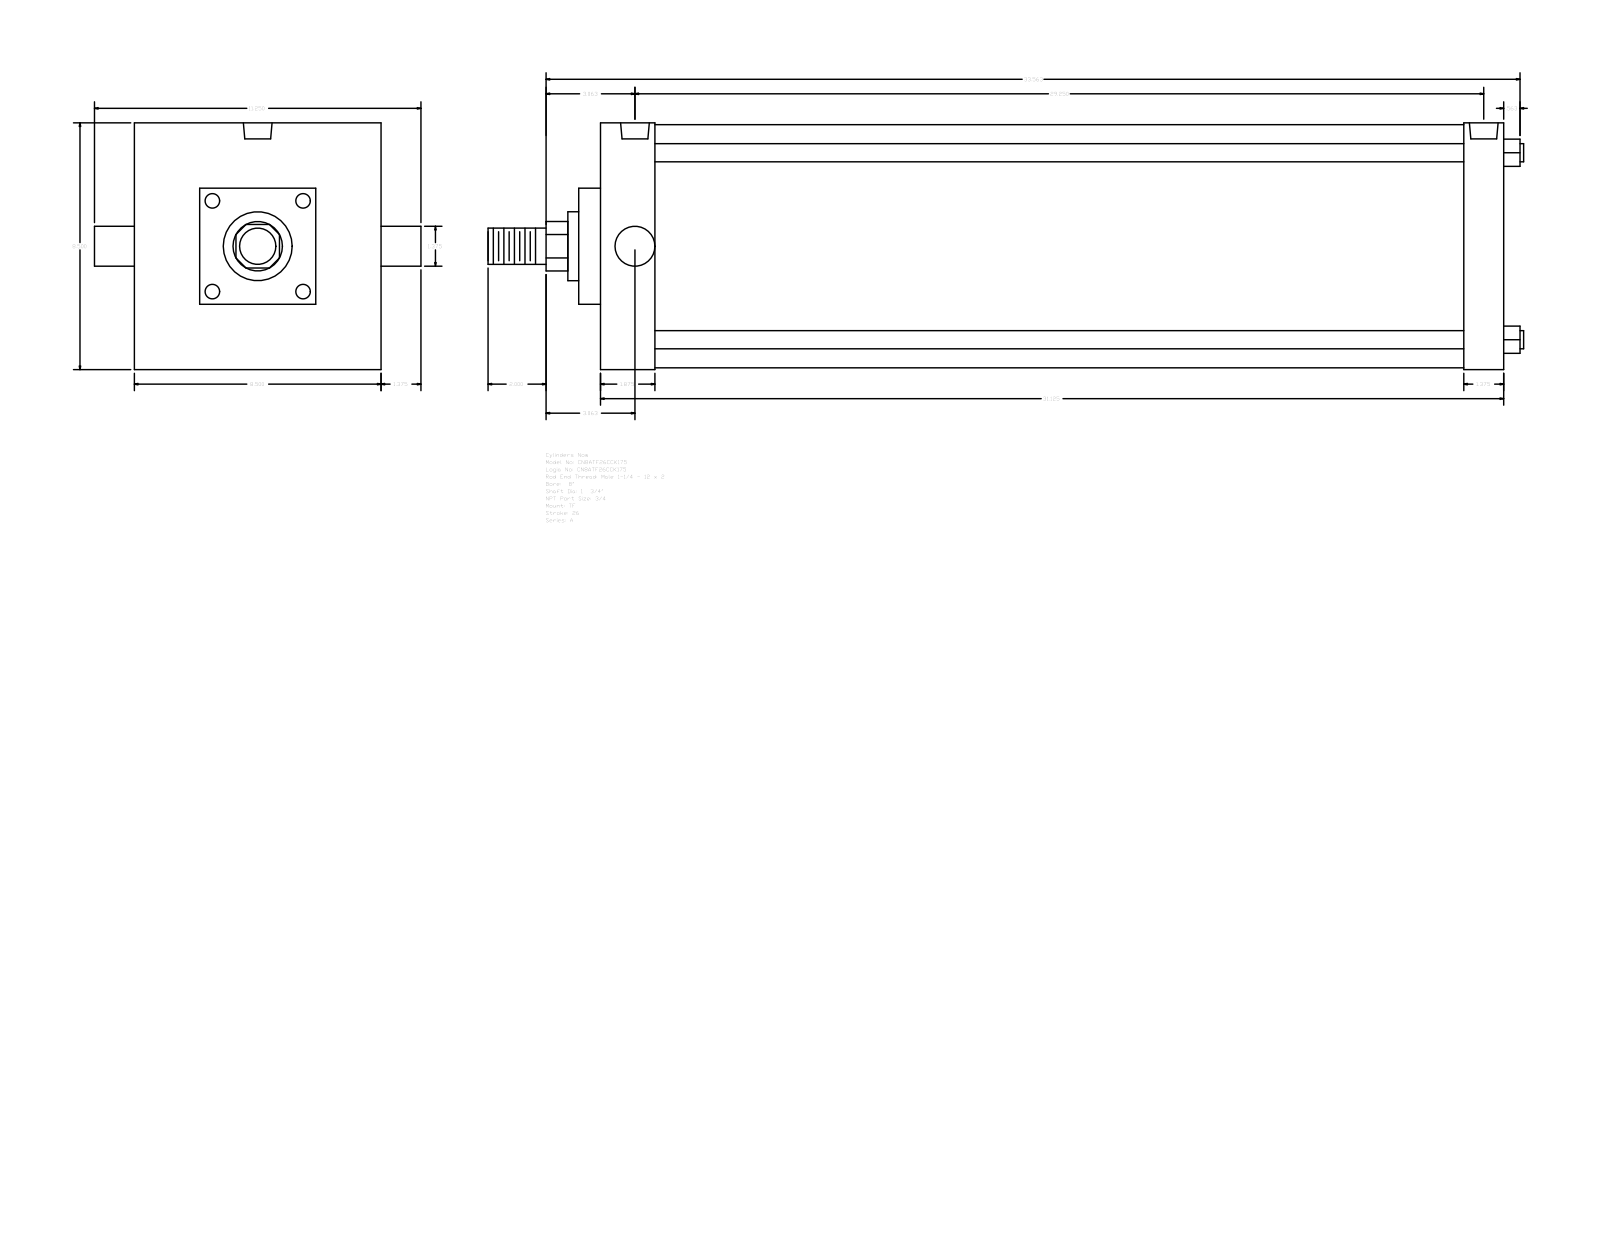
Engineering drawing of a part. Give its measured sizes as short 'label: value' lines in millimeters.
name: A_TF__0800_1.75
written by: GSSL Pune (CONFIG_CONTROL_DESIGN)
unit: mm
bodies: 0 solids, 89 faces (65 planar, 24 cylindrical, 0 other)
size: 906.46 × 285.75 × 215.9
holes: 3× ⌀15.08, 2× ⌀25.12
bosses: 4× ⌀15.88, 1× ⌀212.72, 1× ⌀60.33, 1× ⌀44.45, 1× ⌀34.92, 1× ⌀31.75
rounds: 1× R21.63
face distances: 790.58, 215.9, 34.93, 47.63, 742.95, 755.65, 708.02, 19.05, 57.15, 158.75
hole spacings: 6.35, 736.6, 730.25, 742.95
